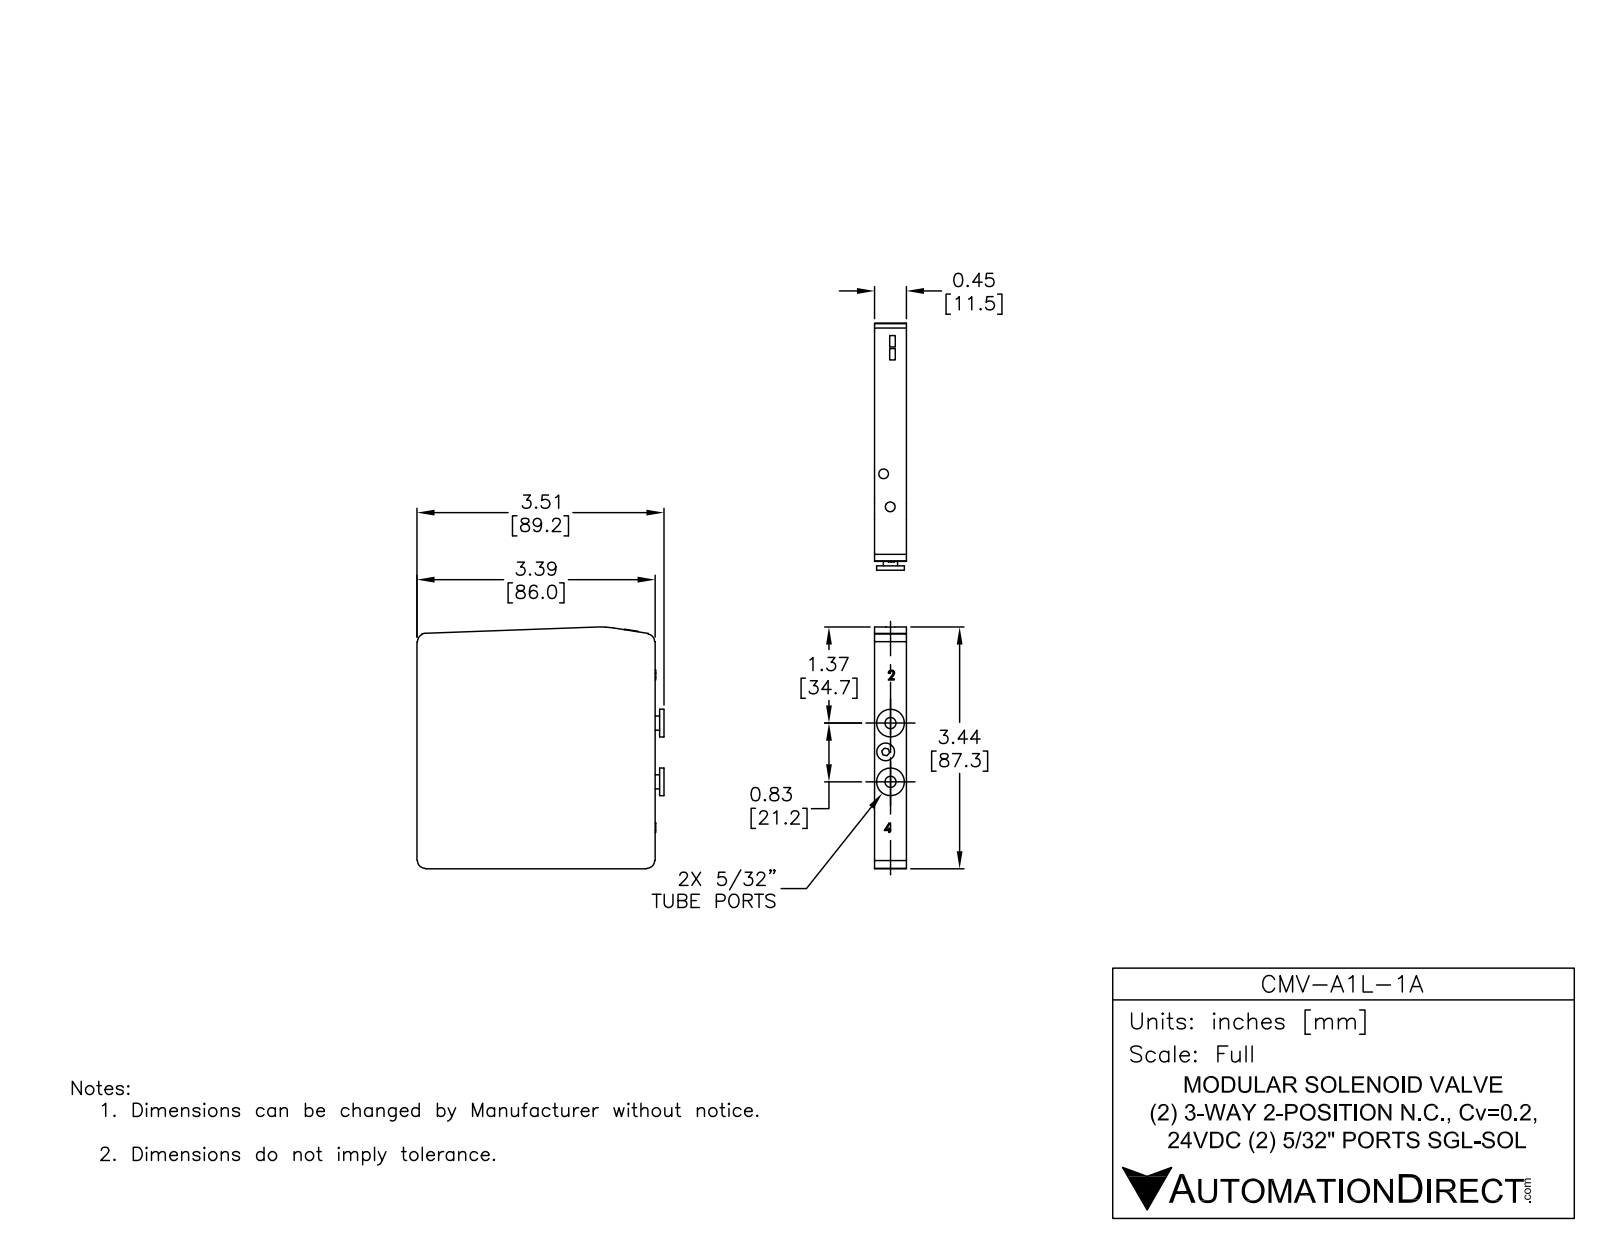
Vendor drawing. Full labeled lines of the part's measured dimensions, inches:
Part name (STEP PRODUCT): CMV-A1L-1A
STEP written by: SolidWorks 2013 (AUTOMOTIVE_DESIGN)
Units: inches
Bodies: 78 solids, 1133 faces (884 planar, 162 cylindrical, 87 other)
Overall size (bounding box): 3.524 × 3.437 × 0.804
Volume: 4.764 in³ · Surface area: 68.55 in²
Round holes (diameter × count): ⌀0.207 ×4, ⌀0.256 ×4, ⌀0.132 ×2, ⌀0.173 ×2, ⌀0.315 ×2, ⌀0.374 ×2, ⌀0.142 ×1, ⌀0.246 ×1, ⌀0.252 ×1
Round bosses / shafts (diameter × count): ⌀0.059 ×4, ⌀0.425 ×2, ⌀0.305 ×2, ⌀0.246 ×2, ⌀0.226 ×2, ⌀0.165 ×2, ⌀0.157 ×2, ⌀0.138 ×1
Partial cylindrical surfaces — rounded edges, fillets, slot ends (radius × count): R0.093 ×12, R0.031 ×4, R0.059 ×4, R0.11 ×4, R0.006 ×2, R0.01 ×2, R0.039 ×2, R0.089 ×2
Main face-to-face distances: 0.453, 0.059, 0.394, 0.039, 0.118, 3.268, 0.098, 0.492, 0.426, 0.466
Hole centre spacings: 0.382, 0.781, 0.873, 0.341, 0.342, 0.372, 0.409, 0.419
